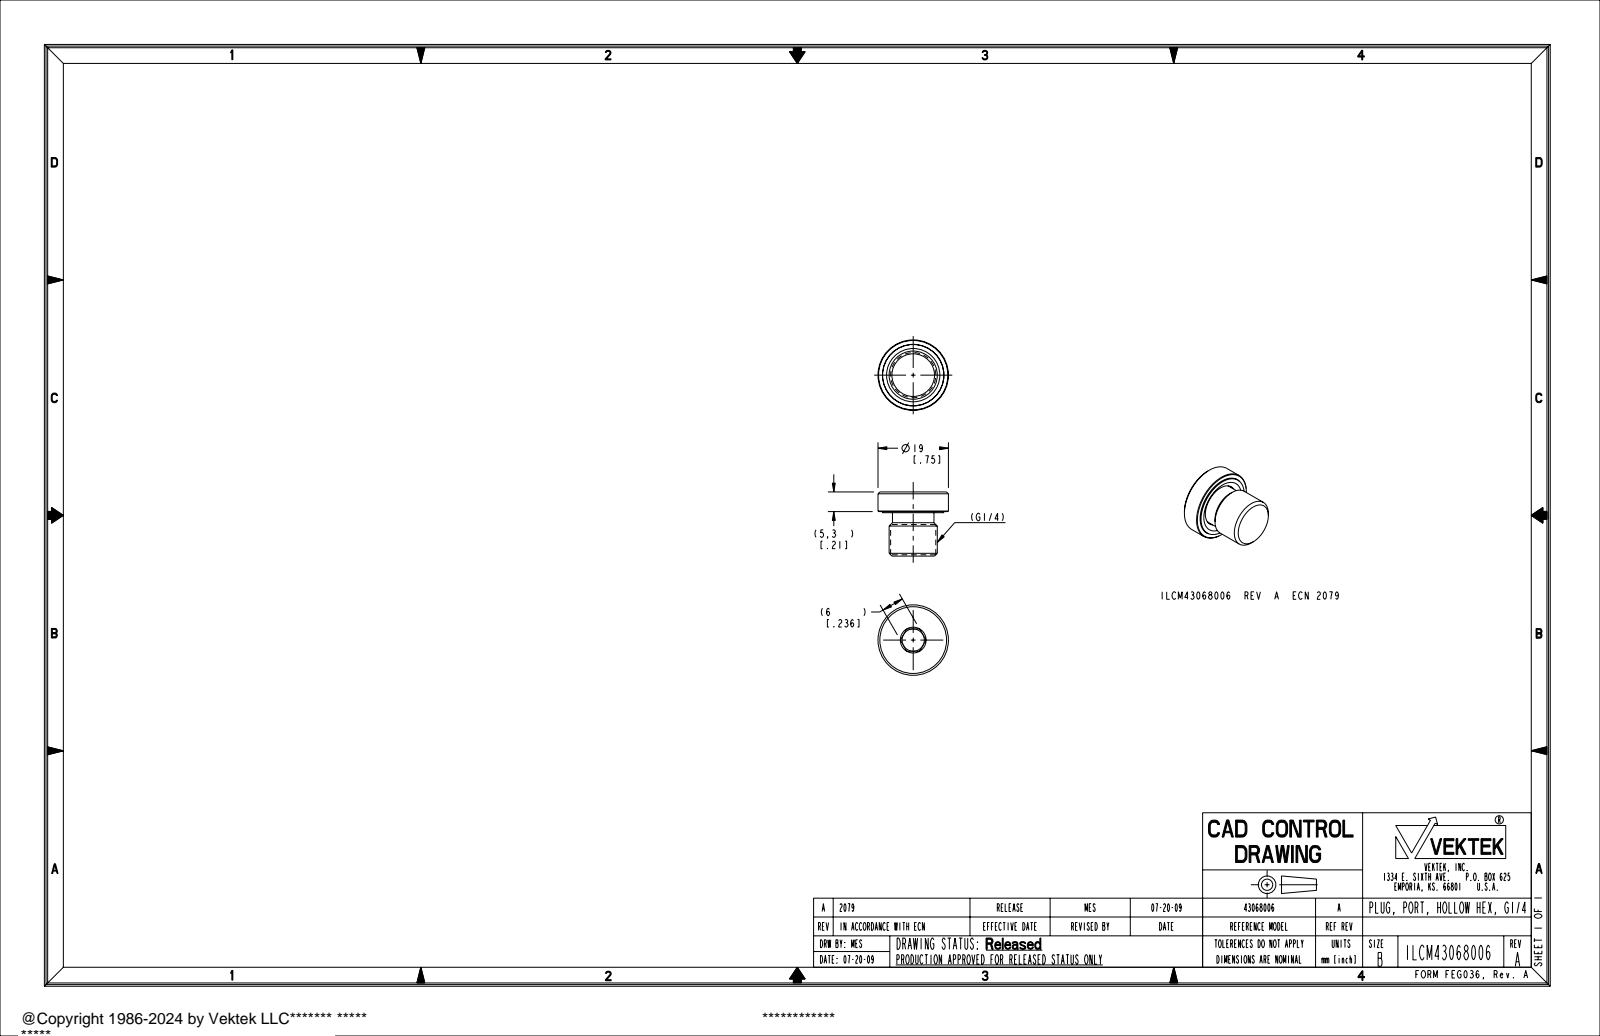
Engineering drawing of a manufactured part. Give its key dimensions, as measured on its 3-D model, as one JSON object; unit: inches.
{"part_name": "ILCM43068006", "step_written_by": "PRO/ENGINEER BY PARAMETRIC TECHNOLOGY CORPORATION, 2007460 (AUTOMOTIVE_DESIGN_CC2)", "units": "inches", "bodies": {"solids": 1, "faces": 48, "planar": 18, "cylindrical": 14, "other": 16}, "overall_size": [0.748, 0.748, 0.681], "volume_in3": 0.168, "surface_area_in2": 3.124, "round_holes": [[0.457, 1], [0.654, 1]], "round_bosses_or_shafts": [[0.748, 1], [0.65, 1], [0.512, 1], [0.48, 1], [0.441, 1]], "face_to_face_distances": [0.681, 0.236, 0.209, 0.472, 0.22, 0.461, 0.161, 0.047, 0.059, 0.52]}
